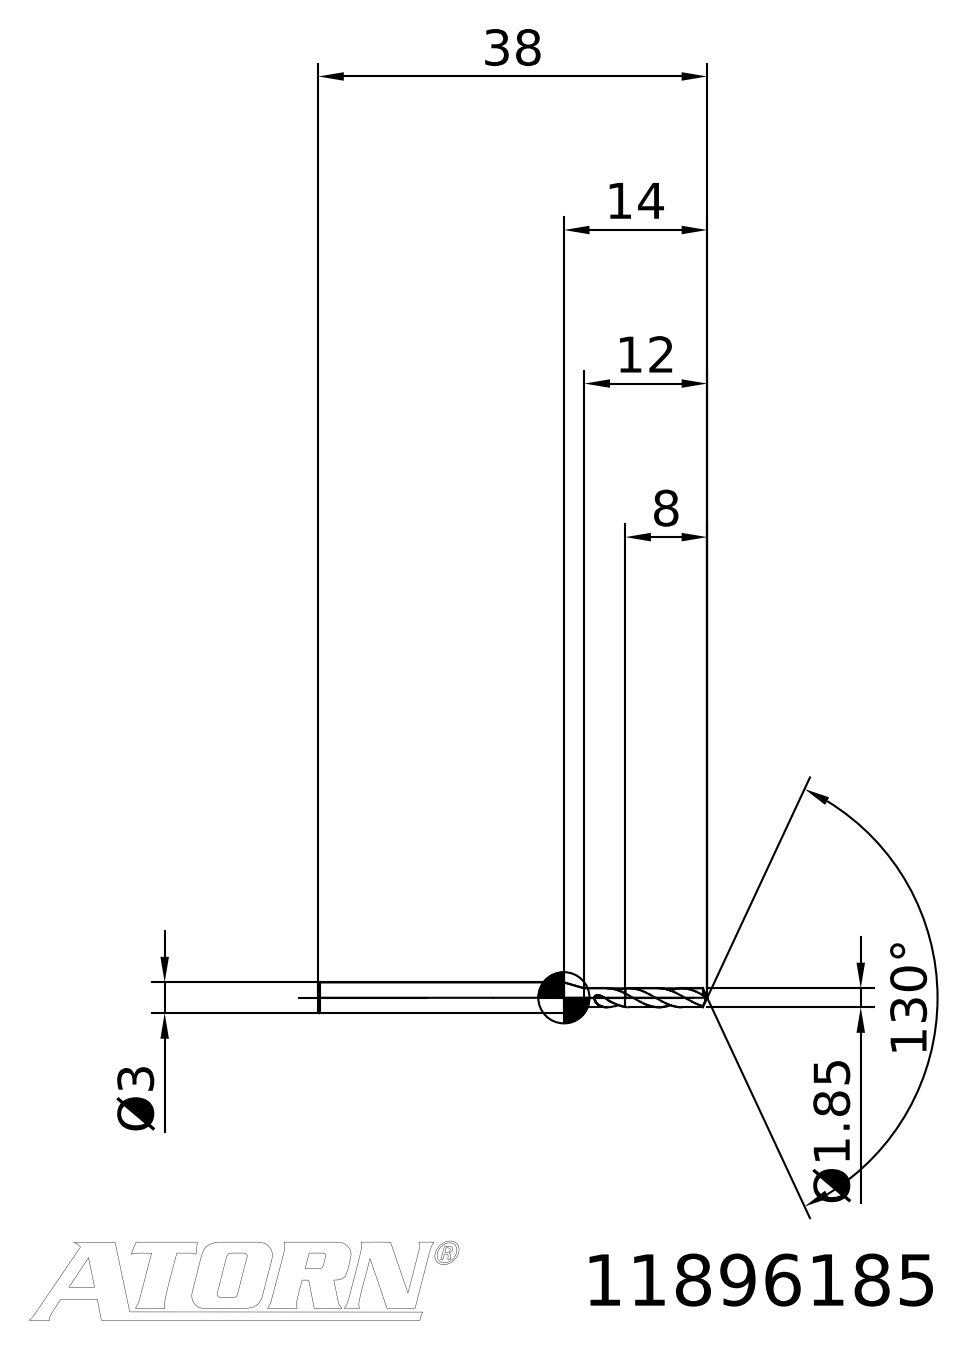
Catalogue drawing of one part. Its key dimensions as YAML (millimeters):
step_written_by: "TDM (AUTOMOTIVE_DESIGN)"
units: millimeters
bodies: {solids: 2, faces: 24, planar: 3, cylindrical: 0, other: 21}
overall_size: [38, 3, 3]
volume: 201
surface_area: 327
face_to_face_distances: [30]
